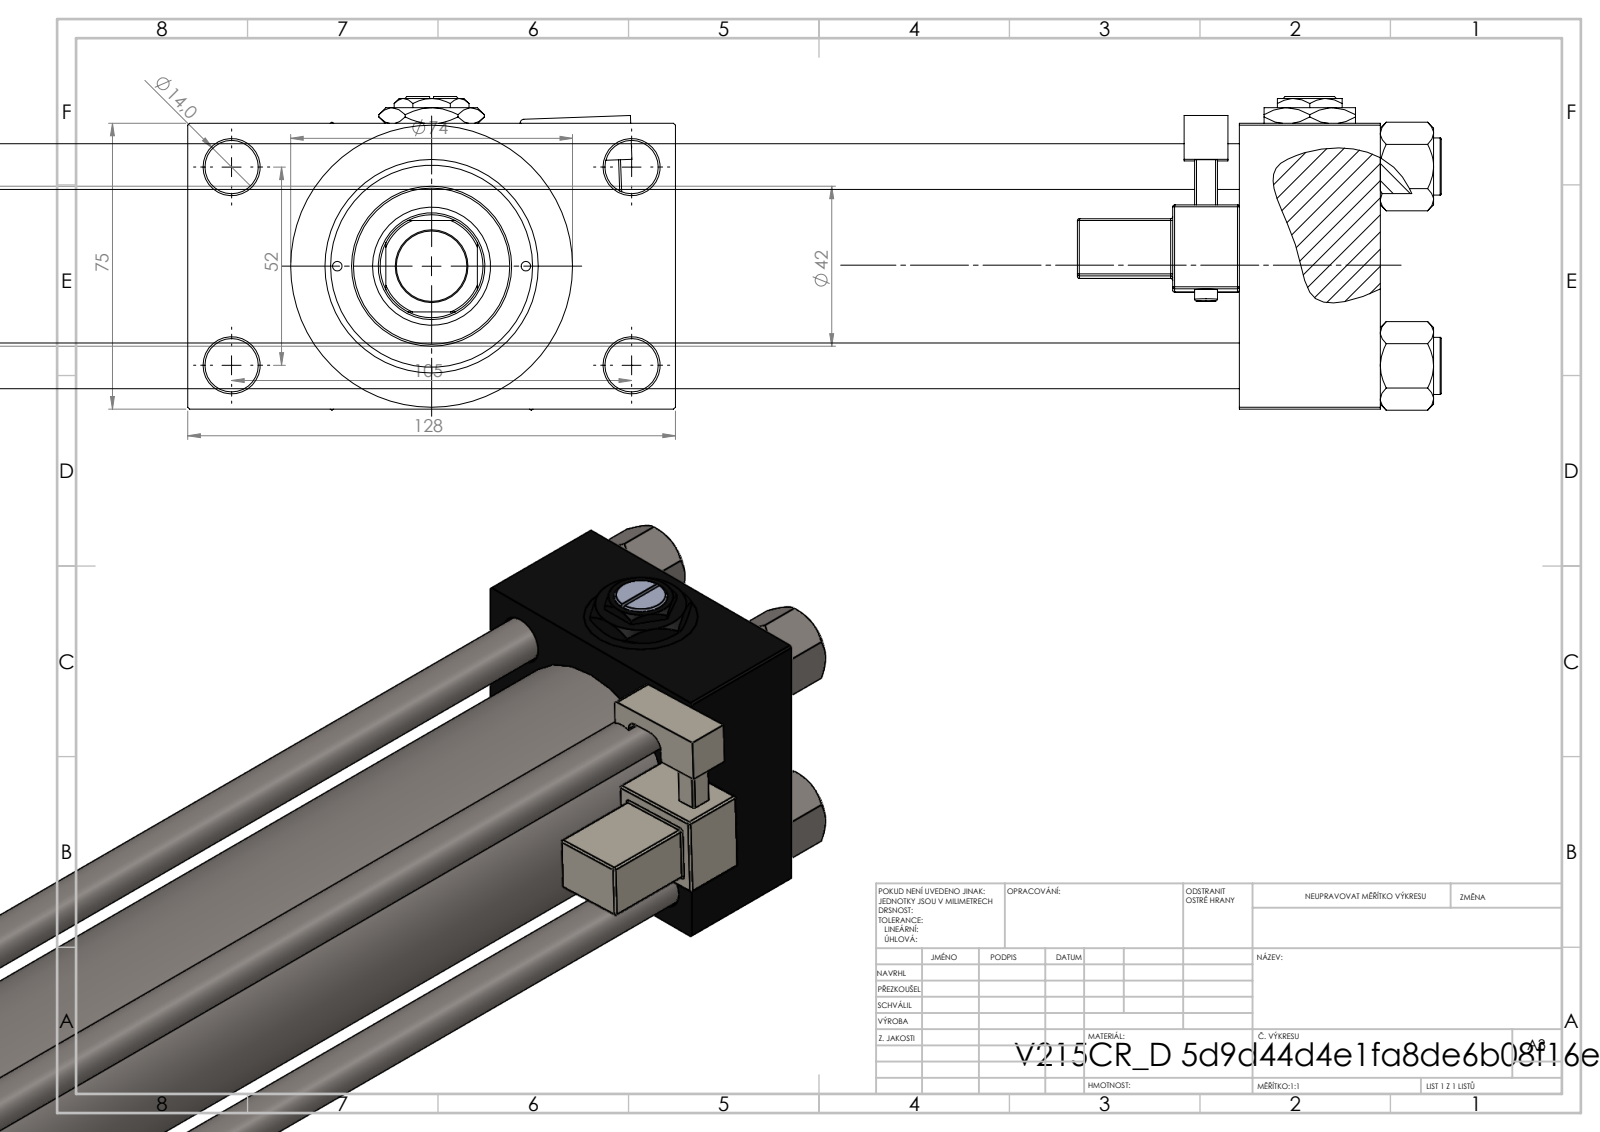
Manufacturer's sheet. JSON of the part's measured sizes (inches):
{"part_name": "Zatka_pro_OIL_PORT; V215CR_D_TYCINKA; V215CR_D_Body; V215CR_VCP_D (+3 more)", "step_written_by": "SolidWorks 2019 (CONFIG_CONTROL_DESIGN)", "units": "inches", "bodies": {"solids": 14, "faces": 1289, "planar": 576, "cylindrical": 133, "other": 580}, "overall_size": [22.638, 5.039, 3.239], "volume_in3": 86.53, "surface_area_in2": 617.2, "round_holes": [[0.472, 4], [0.551, 4], [0.825, 4], [1.181, 4], [0.276, 3], [0.098, 2], [0.728, 1], [1.102, 1], [1.22, 1], [1.614, 1], [1.969, 1], [2.087, 1]], "round_bosses_or_shafts": [[0.591, 4], [2.913, 1], [2.205, 1], [1.654, 1], [0.236, 1]], "partial_cylinders_radius": [[0.02, 24], [0.039, 1], [0.098, 1], [0.157, 1], [0.531, 1]], "face_to_face_distances": [2.953, 17.244, 1.457, 18.701, 1.043, 20.394, 18.937, 1.693, 3.996, 0.63], "hole_center_spacings": [1.031, 1.037, 1.456, 1.497, 2.059, 2.253, 2.3, 2.307]}
